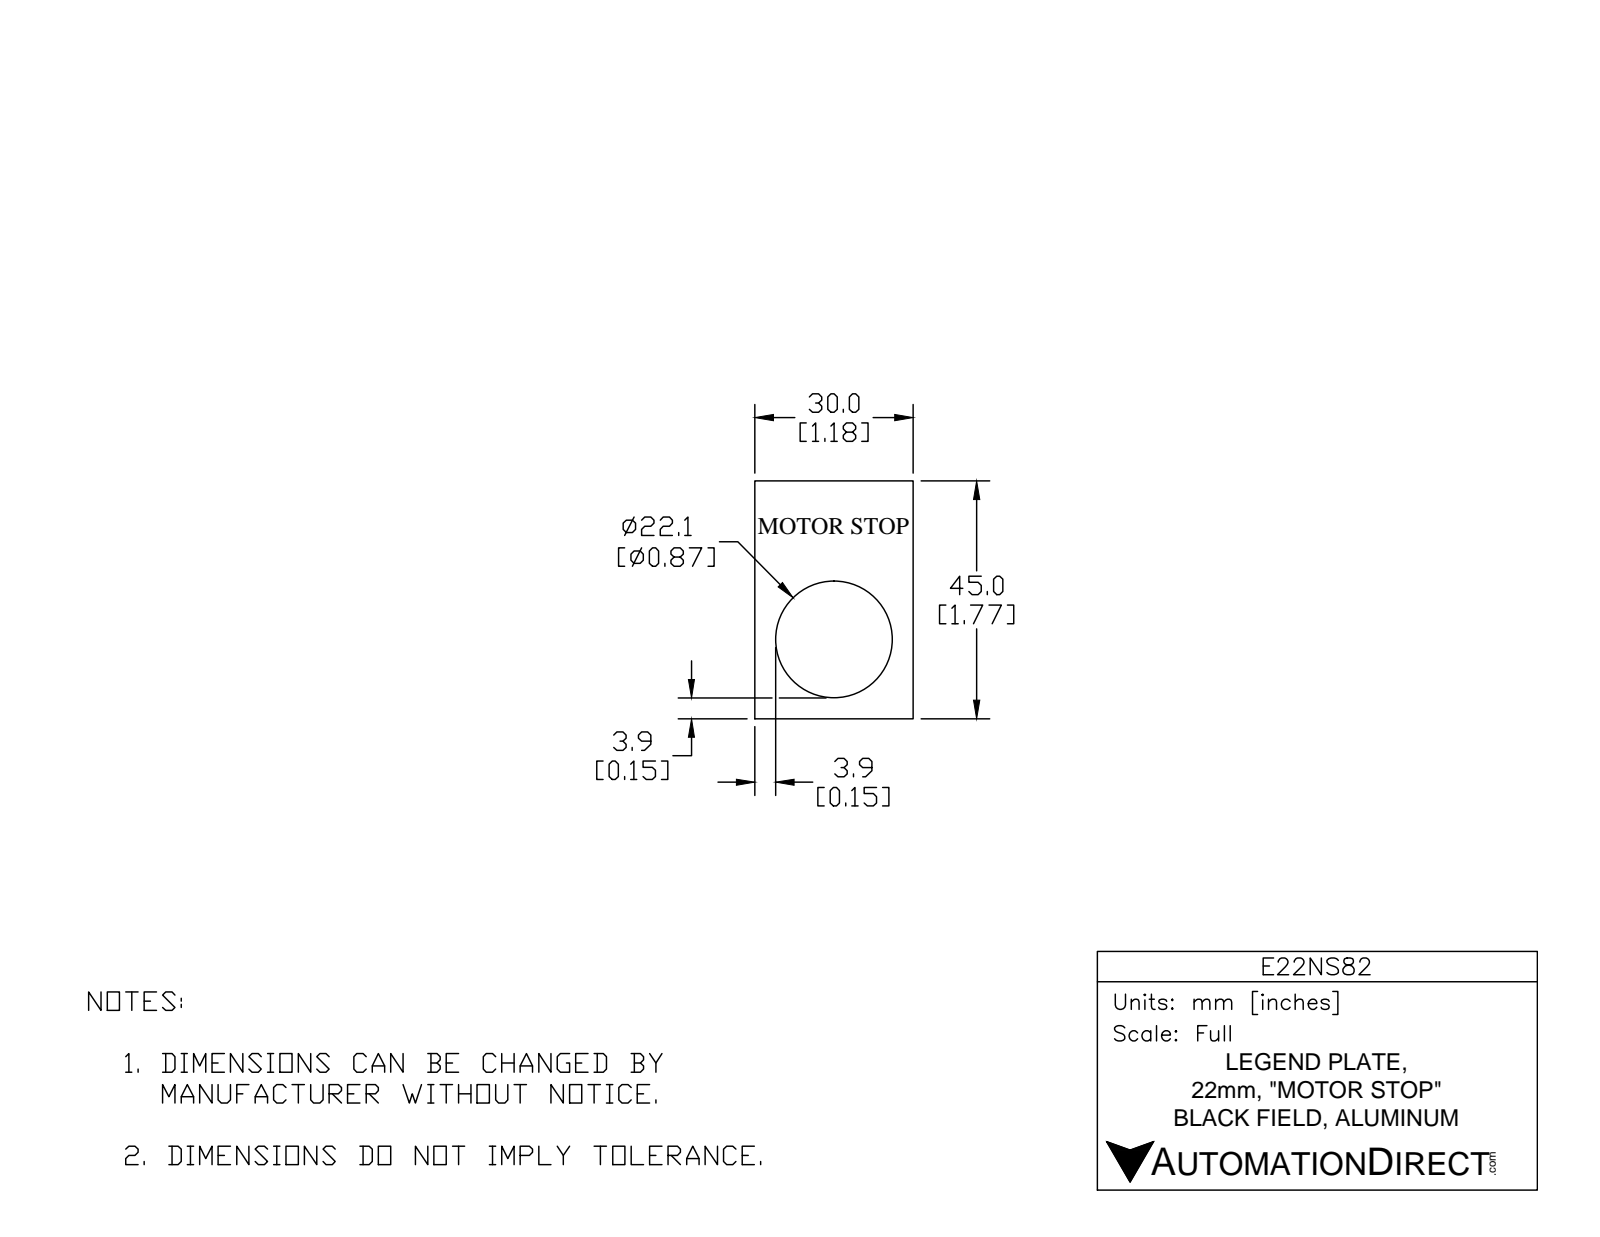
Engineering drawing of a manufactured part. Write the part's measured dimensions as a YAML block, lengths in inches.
part_name: "E22NS82"
step_written_by: "SolidWorks 2017 (AUTOMOTIVE_DESIGN)"
units: inches
bodies: {solids: 1, faces: 126, planar: 73, cylindrical: 3, other: 50}
overall_size: [1.772, 1.181, 0.051]
volume: 0.076
surface_area: 3.494
round_holes:
  - {diameter: 0.874, count: 1}
face_to_face_distances: [0.051, 1.181, 1.772, 0.041, 0.185, 1.587, 0.208, 0.528, 0.654, 0.461]
